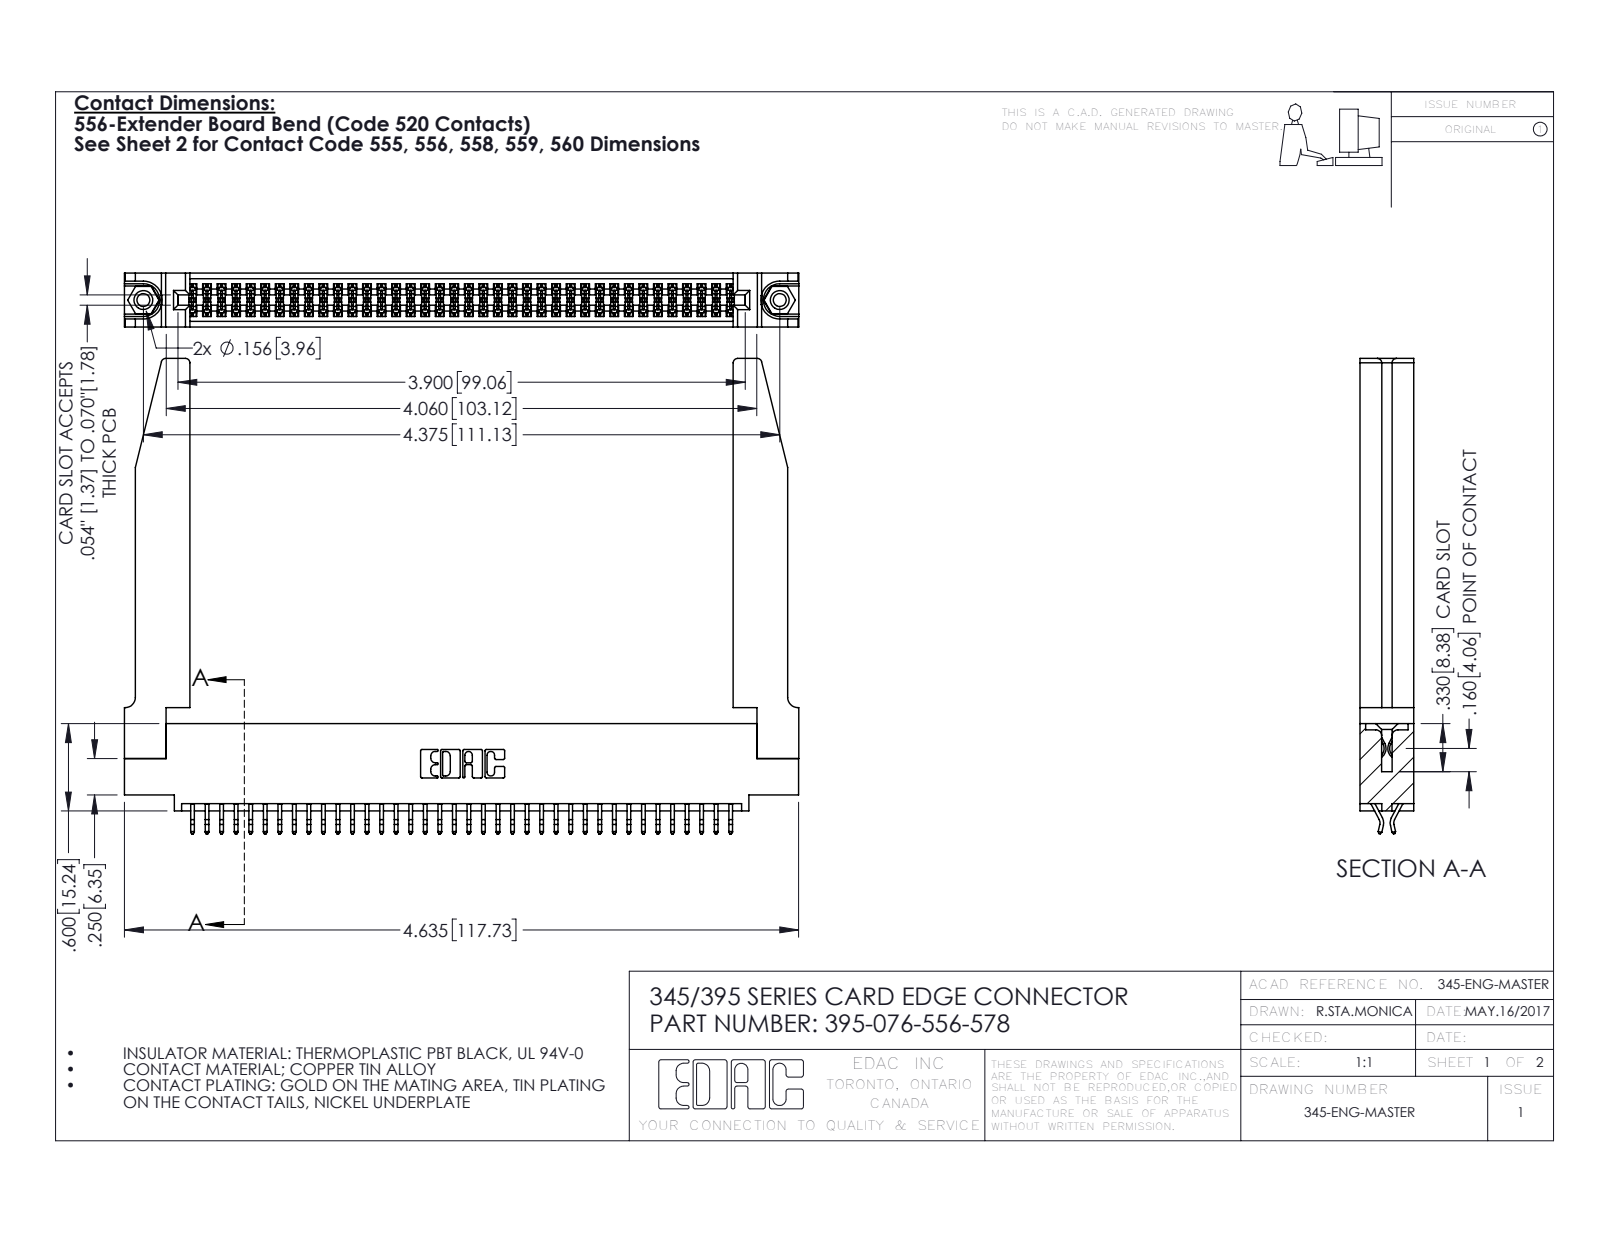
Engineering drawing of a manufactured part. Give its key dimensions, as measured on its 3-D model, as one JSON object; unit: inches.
{"part_name": "345-220-078_345-220-078; 395-076-556-578; 345-250-001_345-250-001-102; 345-292-001_556 Tail (+1 more)", "step_written_by": "SolidWorks 2016 (CONFIG_CONTROL_DESIGN)", "units": "inches", "bodies": {"solids": 81, "faces": 4620, "planar": 3038, "cylindrical": 1530, "other": 52}, "overall_size": [4.636, 3.267, 0.37], "volume_in3": 1.165, "surface_area_in2": 36.47, "round_holes": [[0.089, 2], [0.125, 2], [0.156, 2], [0.064, 1]], "round_bosses_or_shafts": [[0.155, 2]], "partial_cylinders_radius": [[0.006, 114], [0.01, 22], [0.03, 8], [0.007, 6], [0.031, 6], [0.026, 3], [0.01, 2], [0.014, 2]], "face_to_face_distances": [0.37, 0.072, 0.298, 0.025, 0.2, 0.098, 0.272, 0.225, 0.148, 0.15], "hole_center_spacings": [0.27, 4.139, 4.375]}
